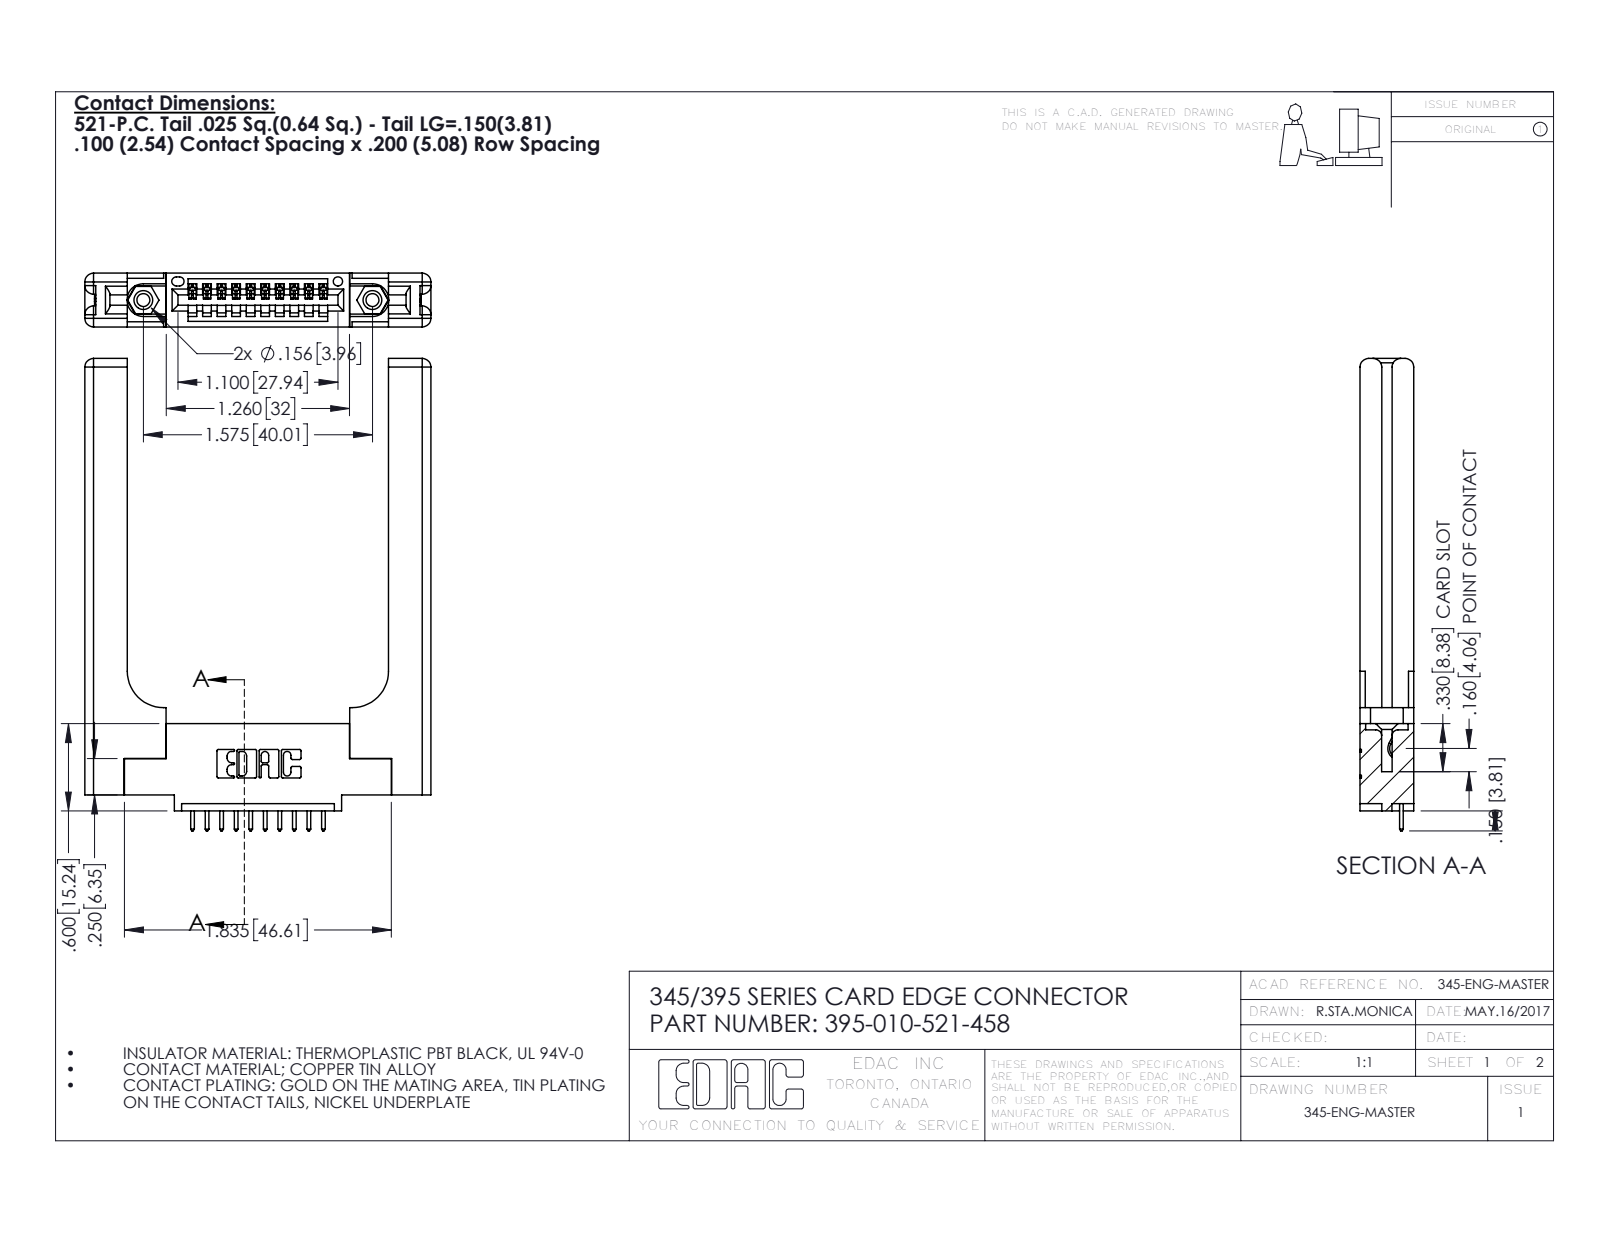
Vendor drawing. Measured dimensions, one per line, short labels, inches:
name: 395-010-521-458; 345-220-058_345-220-058; 345-250-001_345-250-001-102; 345-292-001_345-293-121 (+1 more)
written by: SolidWorks 2016 (CONFIG_CONTROL_DESIGN)
unit: in
bodies: 15 solids, 966 faces (632 planar, 274 cylindrical, 60 other)
size: 3.247 × 2.379 × 0.37
volume: 0.847 in³; area: 18.58 in²
holes: 2× ⌀0.089, 2× ⌀0.125, 2× ⌀0.156, 1× ⌀0.064
bosses: 2× ⌀0.155
rounds: 22× R0.01, 20× R0.006, 20× R0.01, 16× R0.06, 6× R0.007, 6× R0.031, 3× R0.026, 2× R0.03
face distances: 0.37, 0.15, 0.072, 0.22, 0.148, 0.077, 0.298, 1.796, 0.071, 0.292
hole spacings: 0.27, 1.344, 1.575
